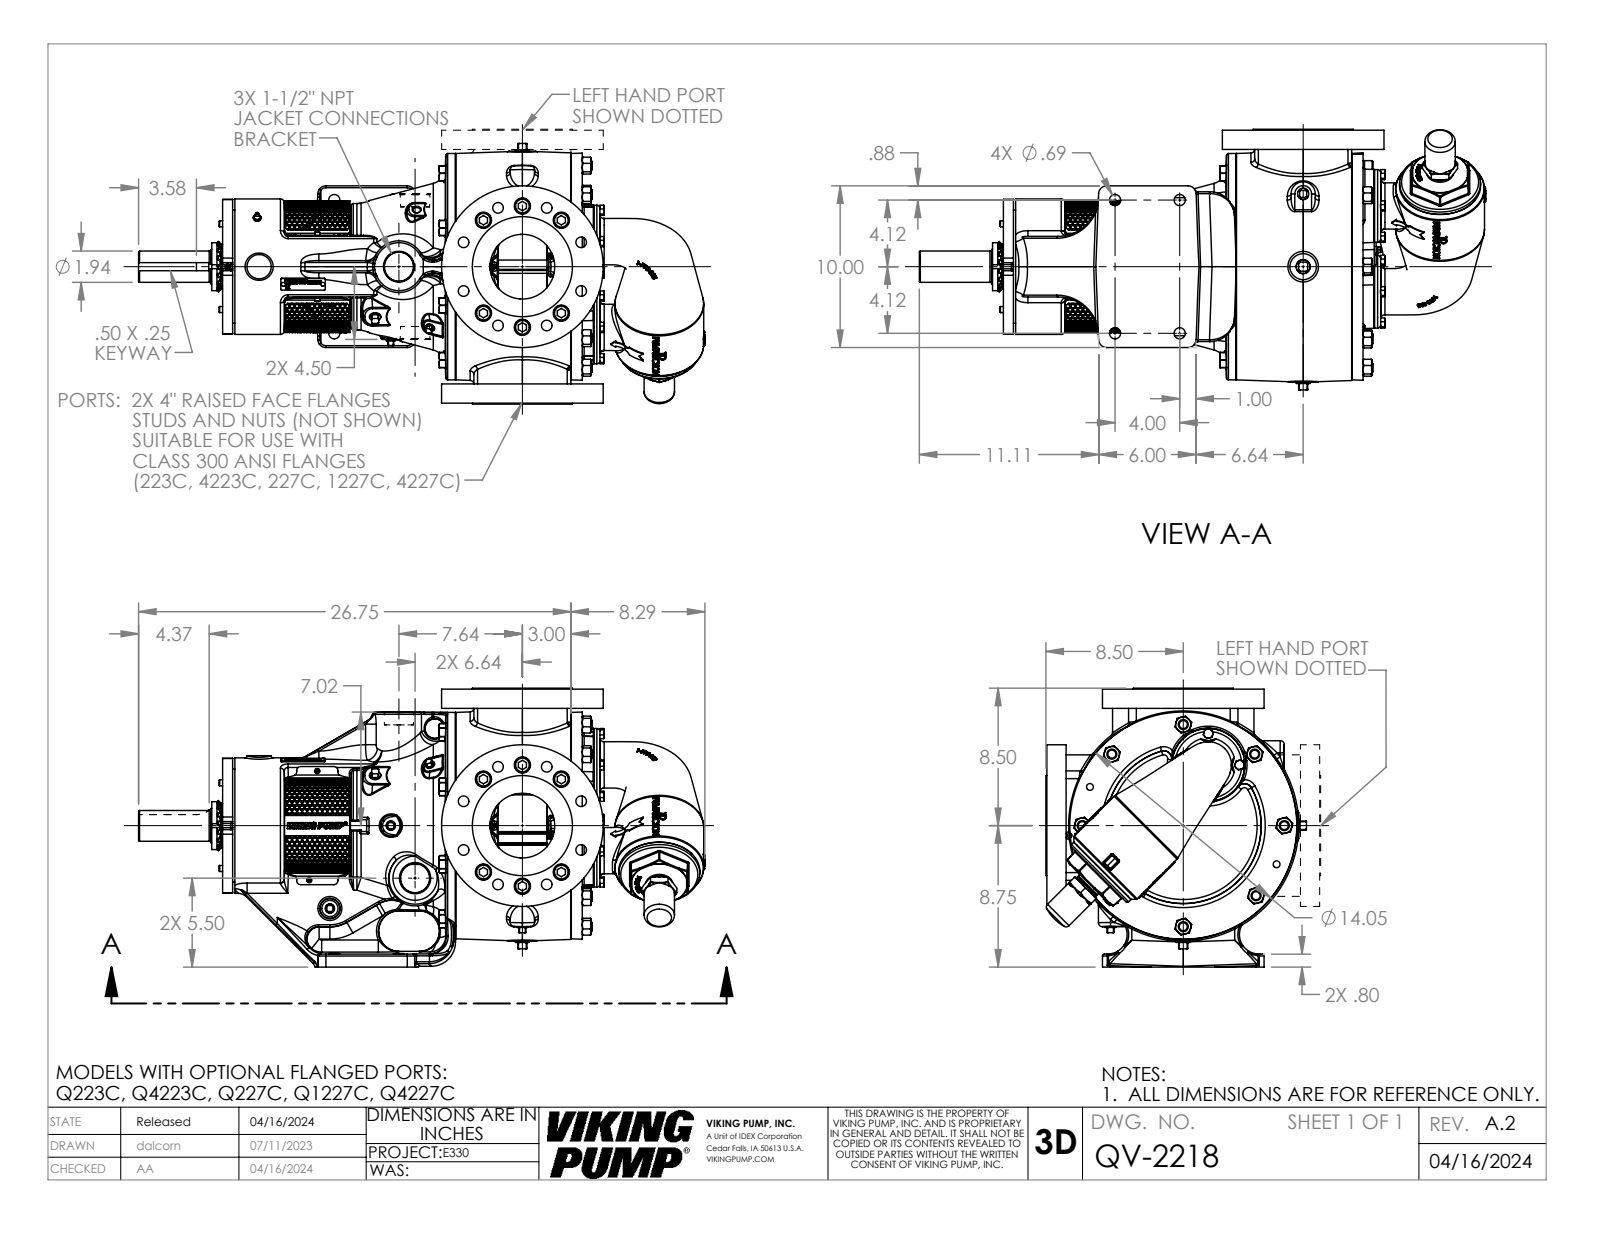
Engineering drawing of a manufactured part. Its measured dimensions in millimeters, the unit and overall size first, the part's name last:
Units: millimetres
Overall size (bounding box): 890 × 438.2 × 409.5
Round holes (diameter × count): ⌀16.7 ×28, ⌀25.4 ×12, ⌀6.4 ×9, ⌀6.8 ×8, ⌀10.3 ×8, ⌀10.4 ×8, ⌀29.4 ×8, ⌀17.5 ×4, ⌀4 ×2, ⌀8 ×2, ⌀8.4 ×2, ⌀10.7 ×2
Round bosses / shafts (diameter × count): ⌀23.8 ×12, ⌀15.9 ×12, ⌀15.7 ×8, ⌀9.5 ×8, ⌀7.9 ×3, ⌀4.8 ×3, ⌀254 ×2, ⌀157.2 ×2
Partial cylindrical surfaces — rounded edges, fillets, slot ends (radius × count): R3 ×52, R1.5 ×34, R12.7 ×22, R0.4 ×18, R2.3 ×18, R6.4 ×18, R1.8 ×16, R19.1 ×16
Main face-to-face distances: 30.2, 95.3, 12.7, 406.4, 436.6, 1.5, 31.8, 552.6, 565.3, 457.3
Hole centre spacings: 95.3, 184.8, 52.8, 100, 30.1, 68.9, 76.5, 76.6
Volume: 42 870 000 mm³ · Surface area: 1 558 000 mm²
Bodies: 1 solid, 4991 faces (1815 planar, 823 cylindrical, 2353 other)
Part name (STEP PRODUCT): QV-2218
STEP written by: SolidWorks 2022 (AUTOMOTIVE_DESIGN)
